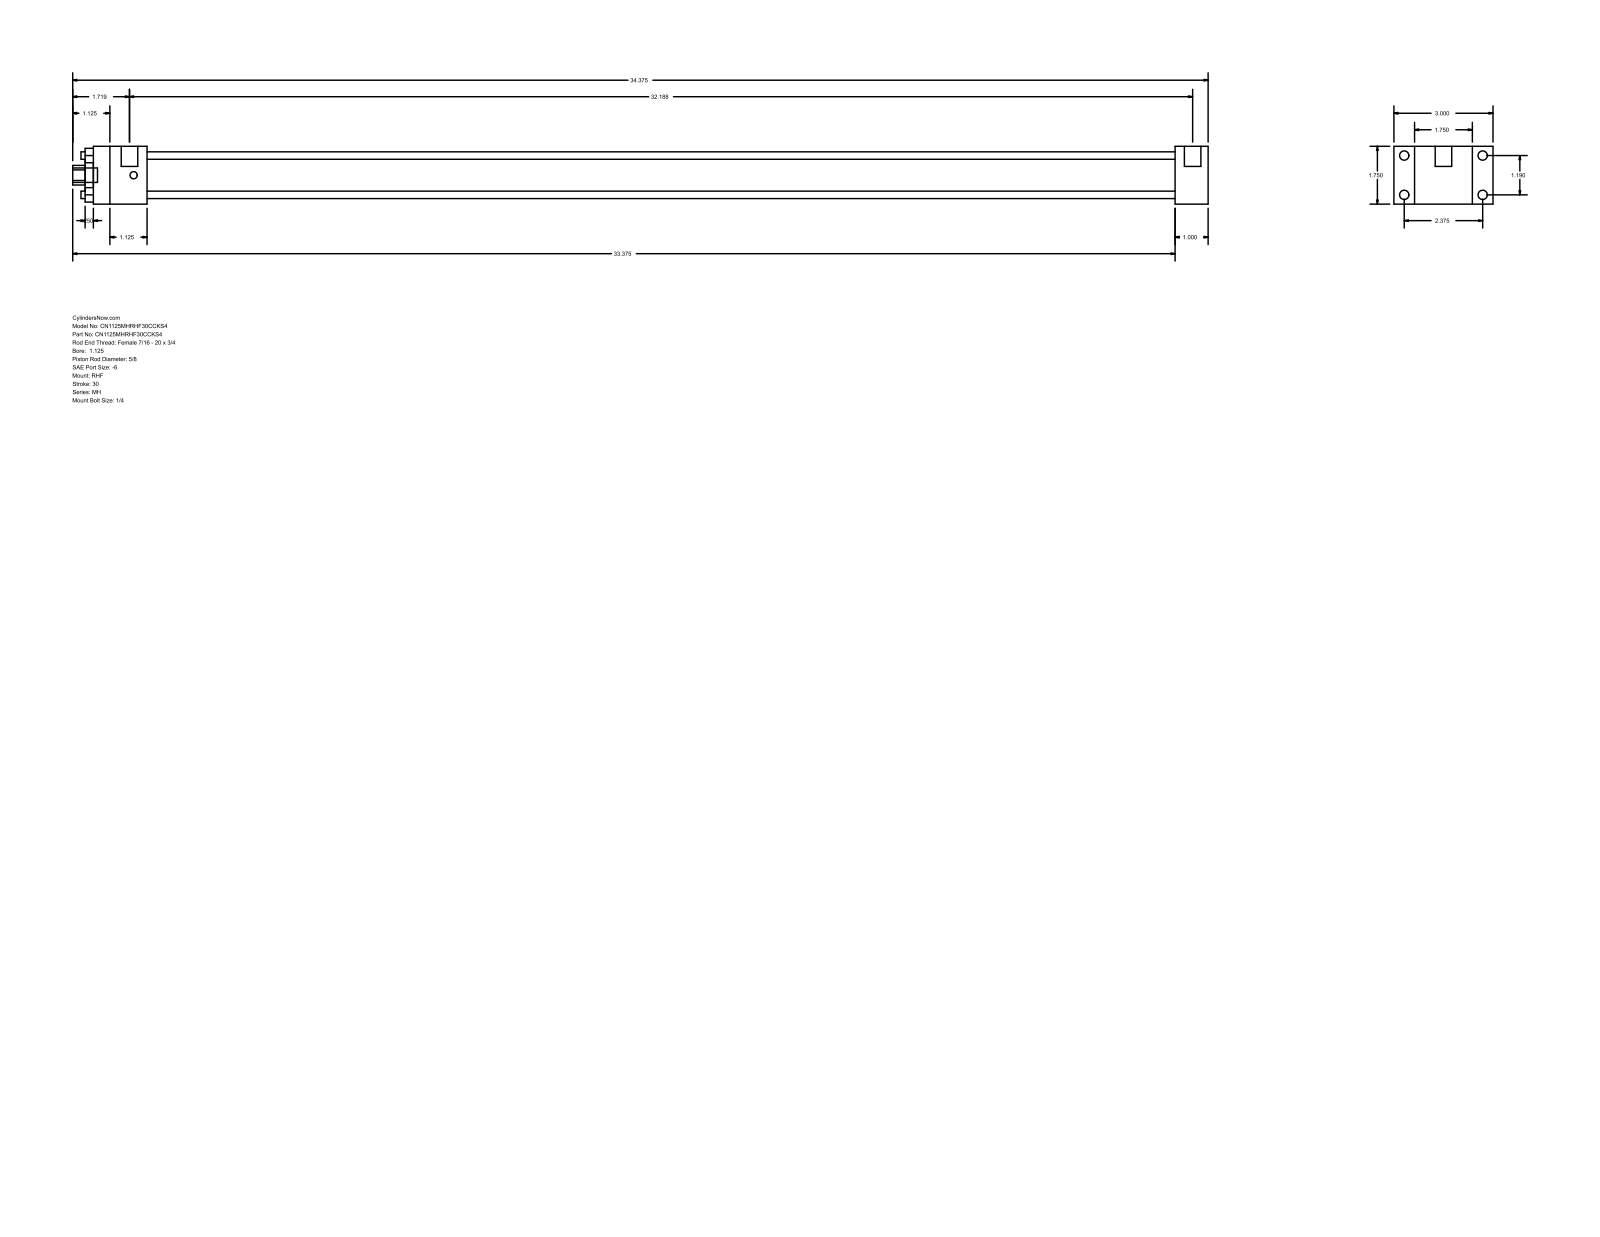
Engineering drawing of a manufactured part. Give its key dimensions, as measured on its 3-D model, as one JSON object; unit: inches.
{"part_name": "MH_RHF__0112_0.625", "step_written_by": "GSSL Pune (CONFIG_CONTROL_DESIGN)", "units": "inches", "bodies": {"solids": 0, "faces": 88, "planar": 60, "cylindrical": 28, "other": 0}, "overall_size": [34.375, 3, 1.75], "round_holes": [[0.225, 4], [0.625, 1], [1.125, 1], [1.375, 1]], "round_bosses_or_shafts": [[0.281, 4], [0.219, 4], [0.5, 2], [0.437, 1]], "partial_cylinders_radius": [[0.297, 1]], "face_to_face_distances": [1.75, 0.625, 2.375, 1, 3, 31.125, 32.125, 1.625, 32.75, 33.75], "hole_center_spacings": [0.841, 1.19, 1.683]}
